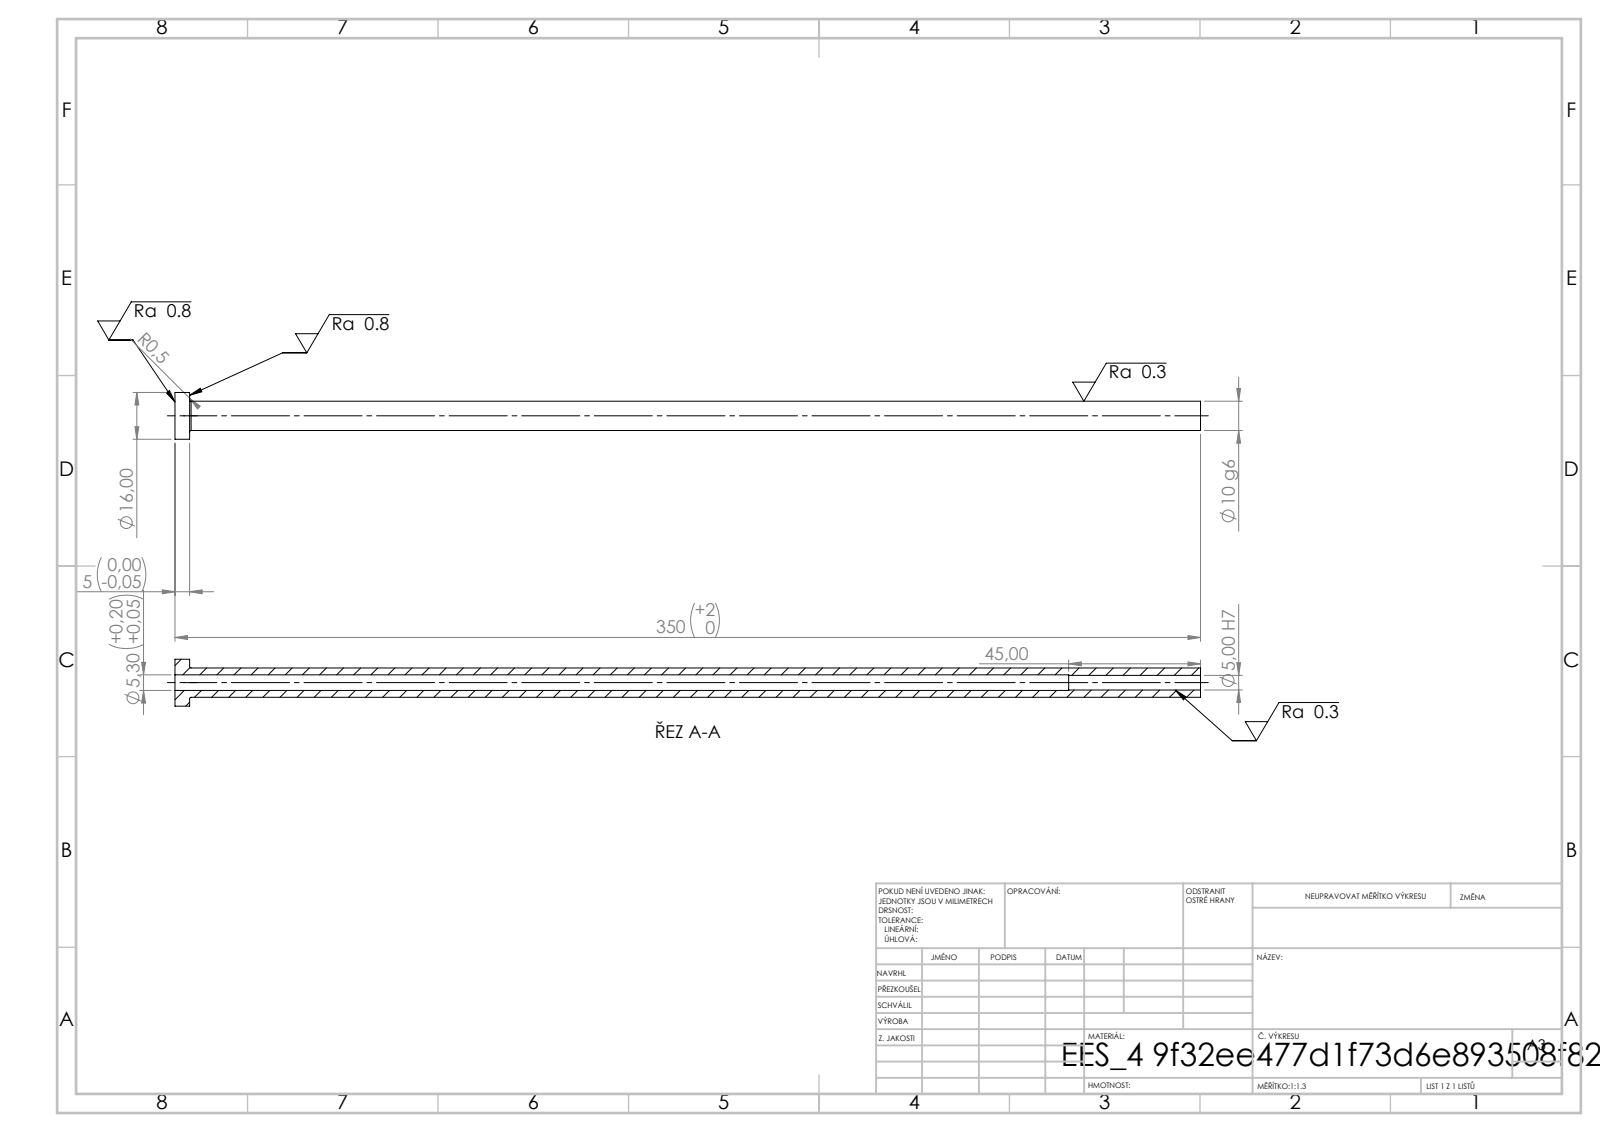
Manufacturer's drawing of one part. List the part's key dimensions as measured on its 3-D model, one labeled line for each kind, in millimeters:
STEP written by: SolidWorks 2019 (CONFIG_CONTROL_DESIGN)
Units: millimetres
Bodies: 1 solid, 14 faces (4 planar, 8 cylindrical, 2 other)
Overall size (bounding box): 350 × 16 × 16
Volume: 20 491 mm³ · Surface area: 17 231 mm²
Round holes (diameter × count): ⌀5 ×1, ⌀5.3 ×1
Round bosses / shafts (diameter × count): ⌀16 ×1, ⌀10 ×1
Main face-to-face distances: 5, 350, 345, 305, 300, 45
